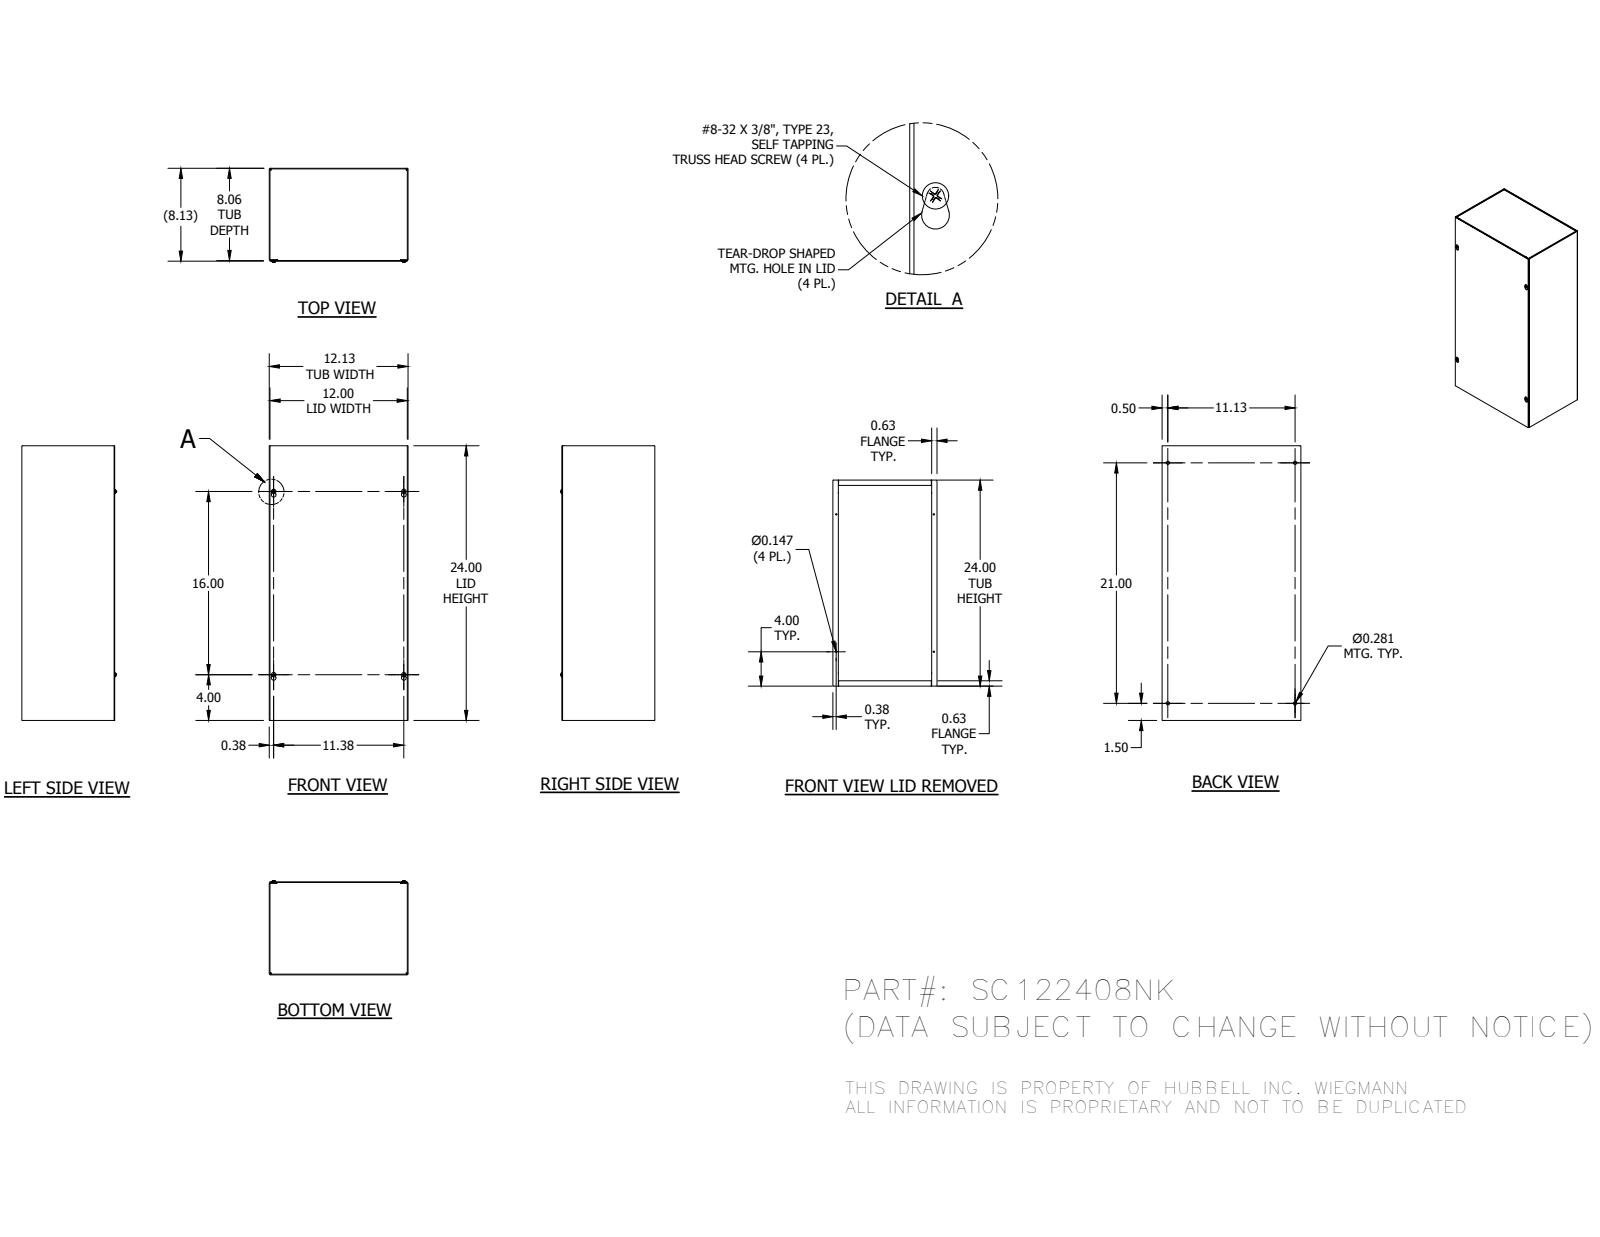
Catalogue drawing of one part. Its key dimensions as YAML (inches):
part_name: "SC122408NKBLR; SC1208NKTB; SC1224LPA; 34056 (+1 more)"
step_written_by: "Autodesk Inventor 2014 (AUTOMOTIVE_DESIGN)"
units: inches
bodies: {solids: 8, faces: 268, planar: 152, cylindrical: 48, other: 68}
overall_size: [24, 12.125, 8.225]
volume: 76.28
surface_area: 2458
round_holes:
  - {diameter: 0.147, count: 4}
  - {diameter: 0.281, count: 4}
round_bosses_or_shafts:
  - {diameter: 0.384, count: 4}
  - {diameter: 0.164, count: 4}
partial_cylinders:
  - {radius: 0.031, count: 12}
  - {radius: 0.094, count: 12}
  - {radius: 0.125, count: 4}
  - {radius: 0.203, count: 4}
face_to_face_distances: [0.063, 12.063, 8, 0.062, 8.062, 8.063, 8.125, 12, 12.125, 23.937]
hole_center_spacings: [2.503, 11.524, 18.5, 21.652, 11.125, 11.375, 16, 19.631]
